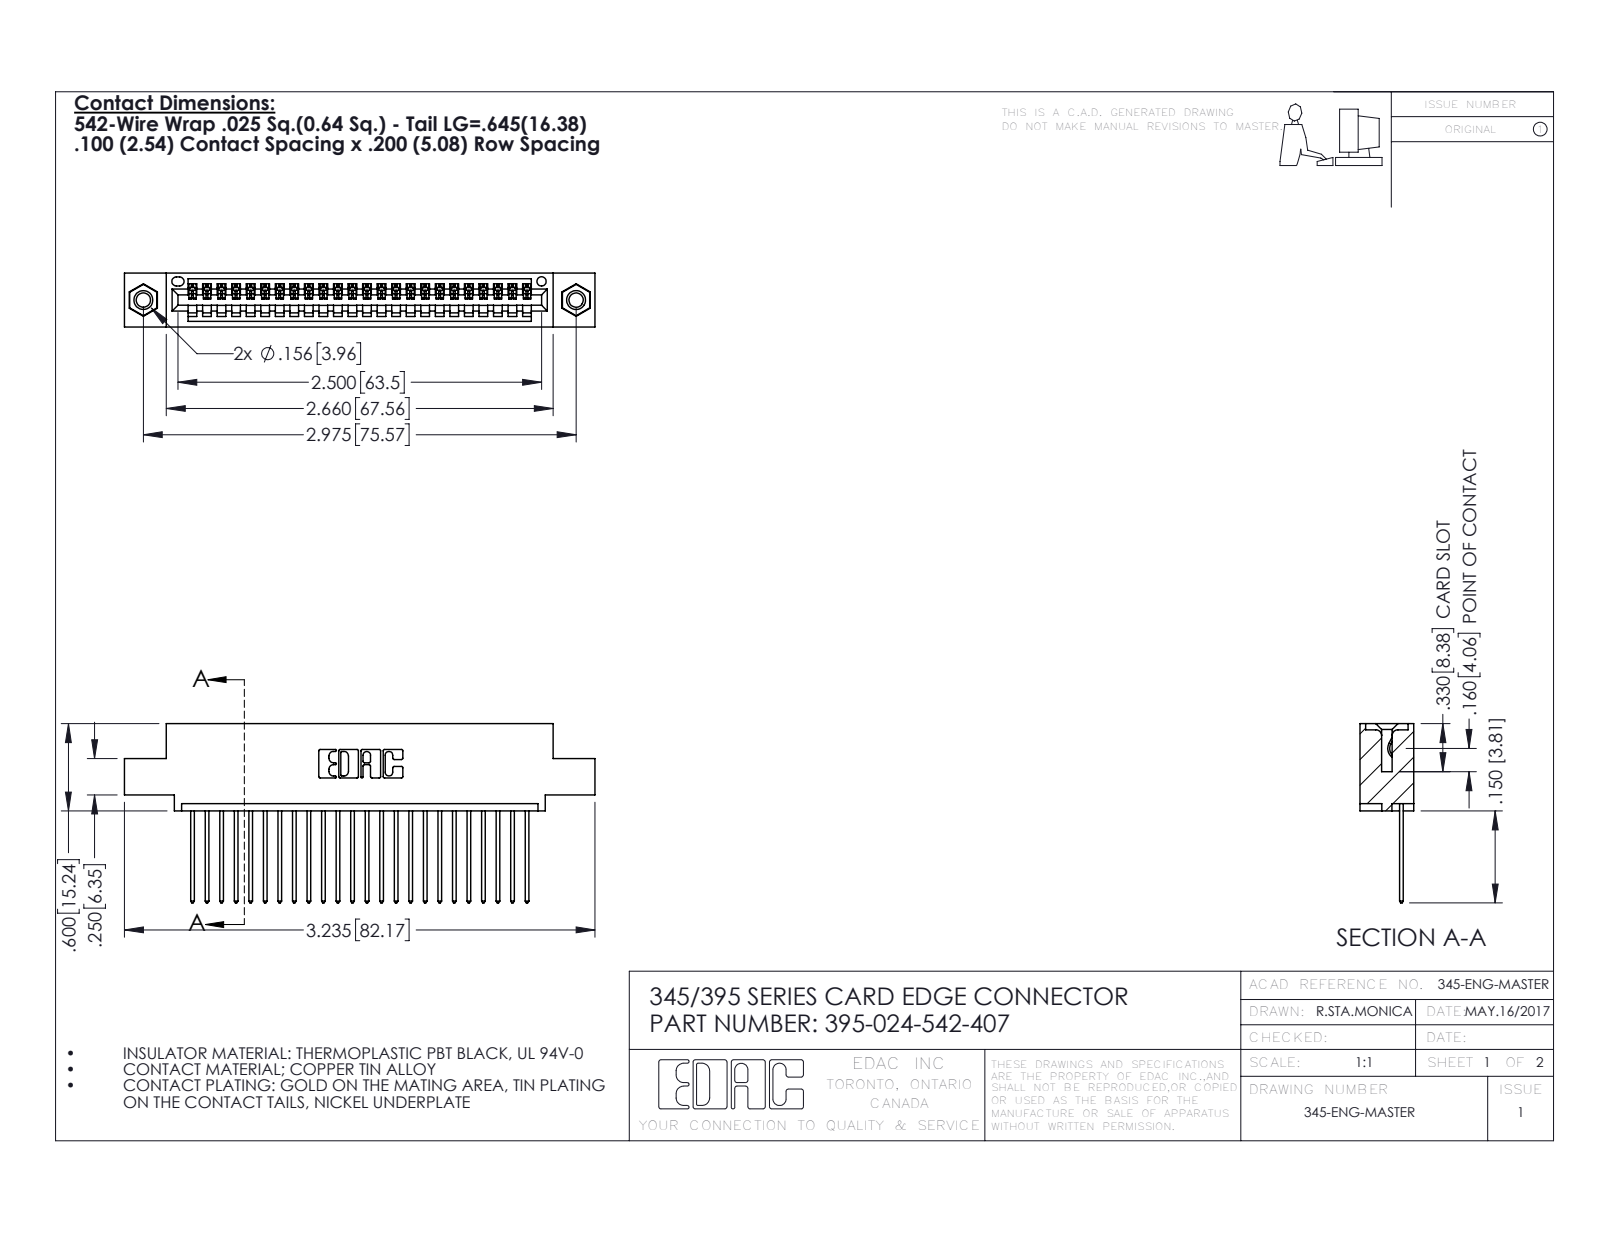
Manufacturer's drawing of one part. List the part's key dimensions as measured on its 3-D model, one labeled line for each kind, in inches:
Part name (STEP PRODUCT): 345 Part_0.110 Offset - 0.156 Dia-TI; 345-292-001_345-293-142; 395-024-542-407; 345-250-001_345-250-005-103
STEP written by: SolidWorks 2016 (CONFIG_CONTROL_DESIGN)
Units: inches
Bodies: 27 solids, 1582 faces (1076 planar, 490 cylindrical, 16 other)
Overall size (bounding box): 3.235 × 1.232 × 0.37
Volume: 0.465 in³ · Surface area: 16.02 in²
Round holes (diameter × count): ⌀0.098 ×2, ⌀0.125 ×2, ⌀0.156 ×2, ⌀0.064 ×1
Round bosses / shafts (diameter × count): ⌀0.155 ×2
Partial cylindrical surfaces — rounded edges, fillets, slot ends (radius × count): R0.006 ×48, R0.01 ×48, R0.01 ×22, R0.007 ×6, R0.031 ×6, R0.026 ×3, R0.031 ×2, R0.04 ×2
Main face-to-face distances: 0.072, 0.298, 0.37, 0.2, 0.098, 0.272, 0.025, 0.225, 0.149, 0.072
Hole centre spacings: 0.27, 2.741, 2.975
